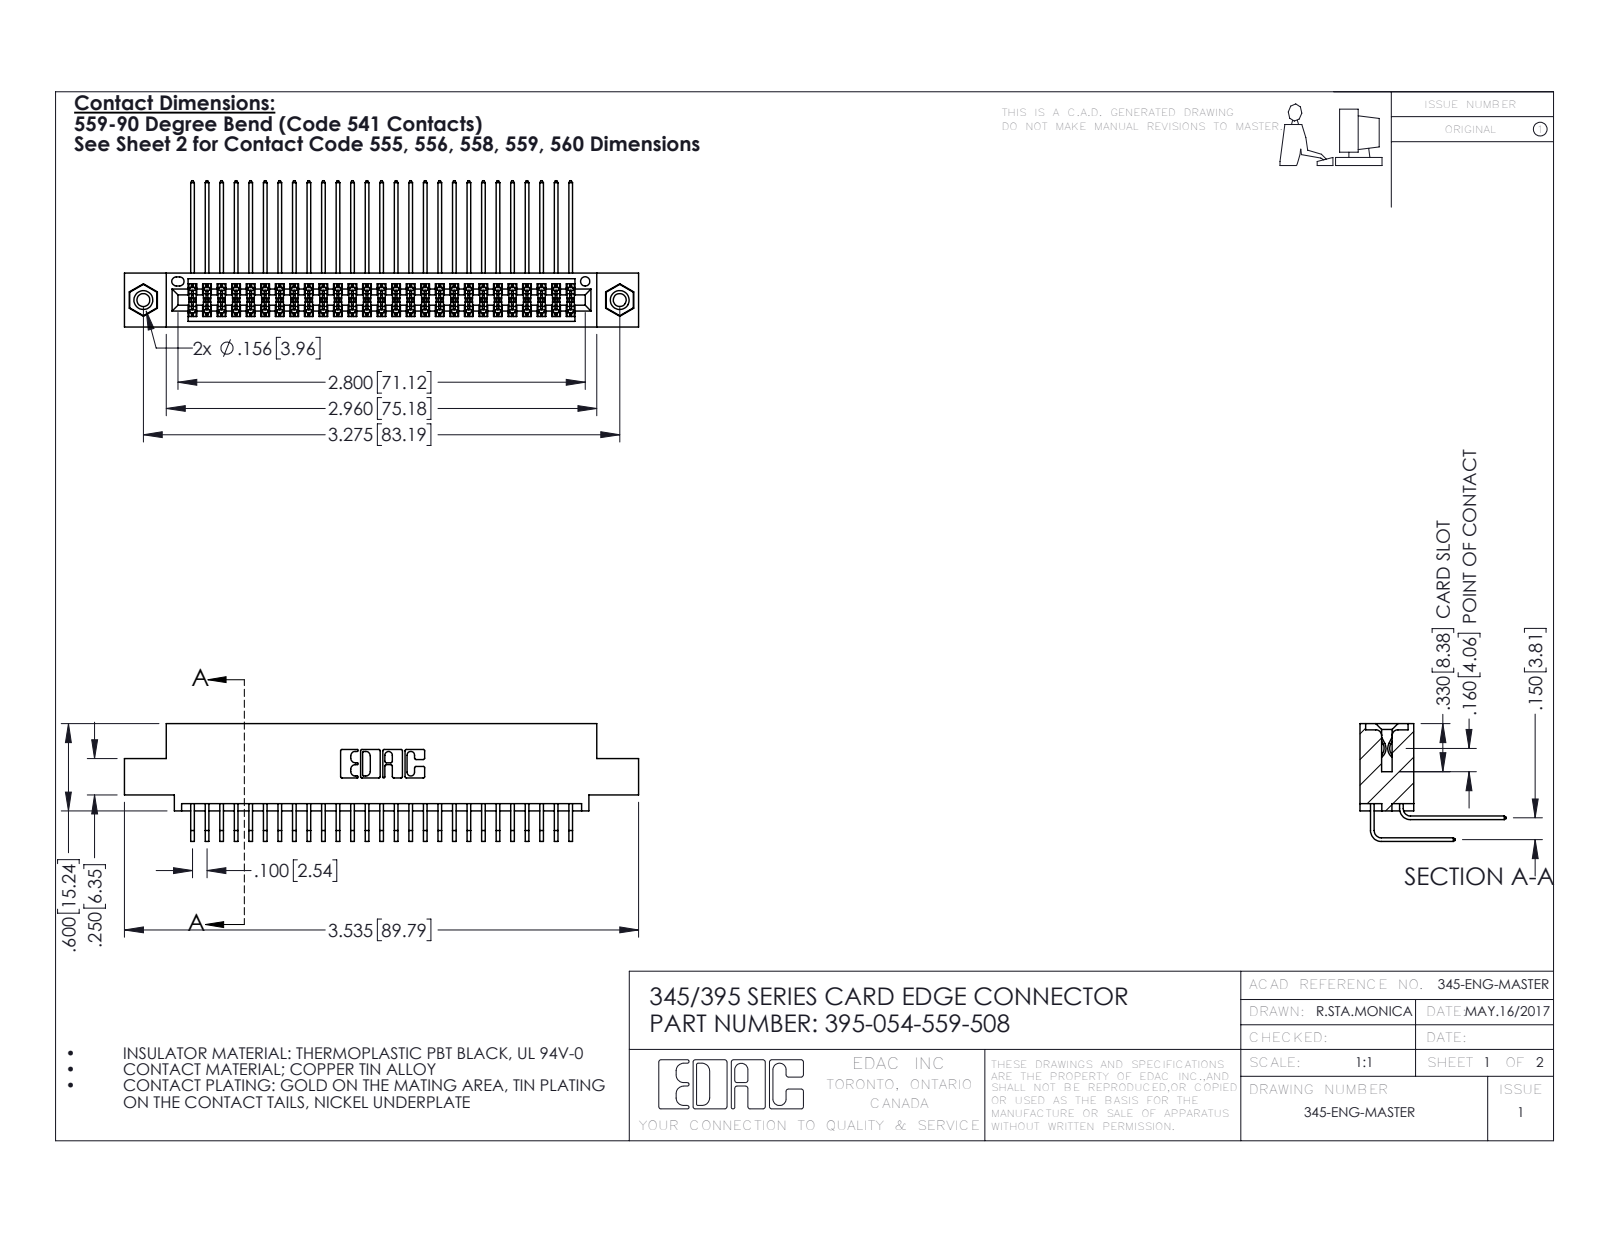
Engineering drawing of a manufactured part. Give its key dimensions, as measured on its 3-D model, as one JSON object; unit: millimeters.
{"part_name": "345 Part_0.110 Offset - 0.156 Dia-TI; 395-054-559-508; 345-292-001_558 559 Tail - 1; 345-250-001_345-250-003-102 (+1 more)", "step_written_by": "SolidWorks 2016 (CONFIG_CONTROL_DESIGN)", "units": "millimeters", "bodies": {"solids": 57, "faces": 2998, "planar": 2006, "cylindrical": 976, "other": 16}, "overall_size": [89.8, 25.5, 20.5], "volume_mm3": 8820, "surface_area_mm2": 14310, "round_holes": [[2.3, 2], [3.2, 2], [4, 2], [1.6, 1]], "round_bosses_or_shafts": [[3.9, 2]], "partial_cylinders_radius": [[0.2, 81], [0.3, 22], [0.2, 6], [0.8, 6], [0.7, 3], [0.4, 2], [0.5, 2], [0.6, 2]], "face_to_face_distances": [1.8, 7.6, 5.1, 9.4, 2.5, 6.9, 0.6, 5.7, 3.8, 4.4], "hole_center_spacings": [6.9, 77.2, 83.2]}
